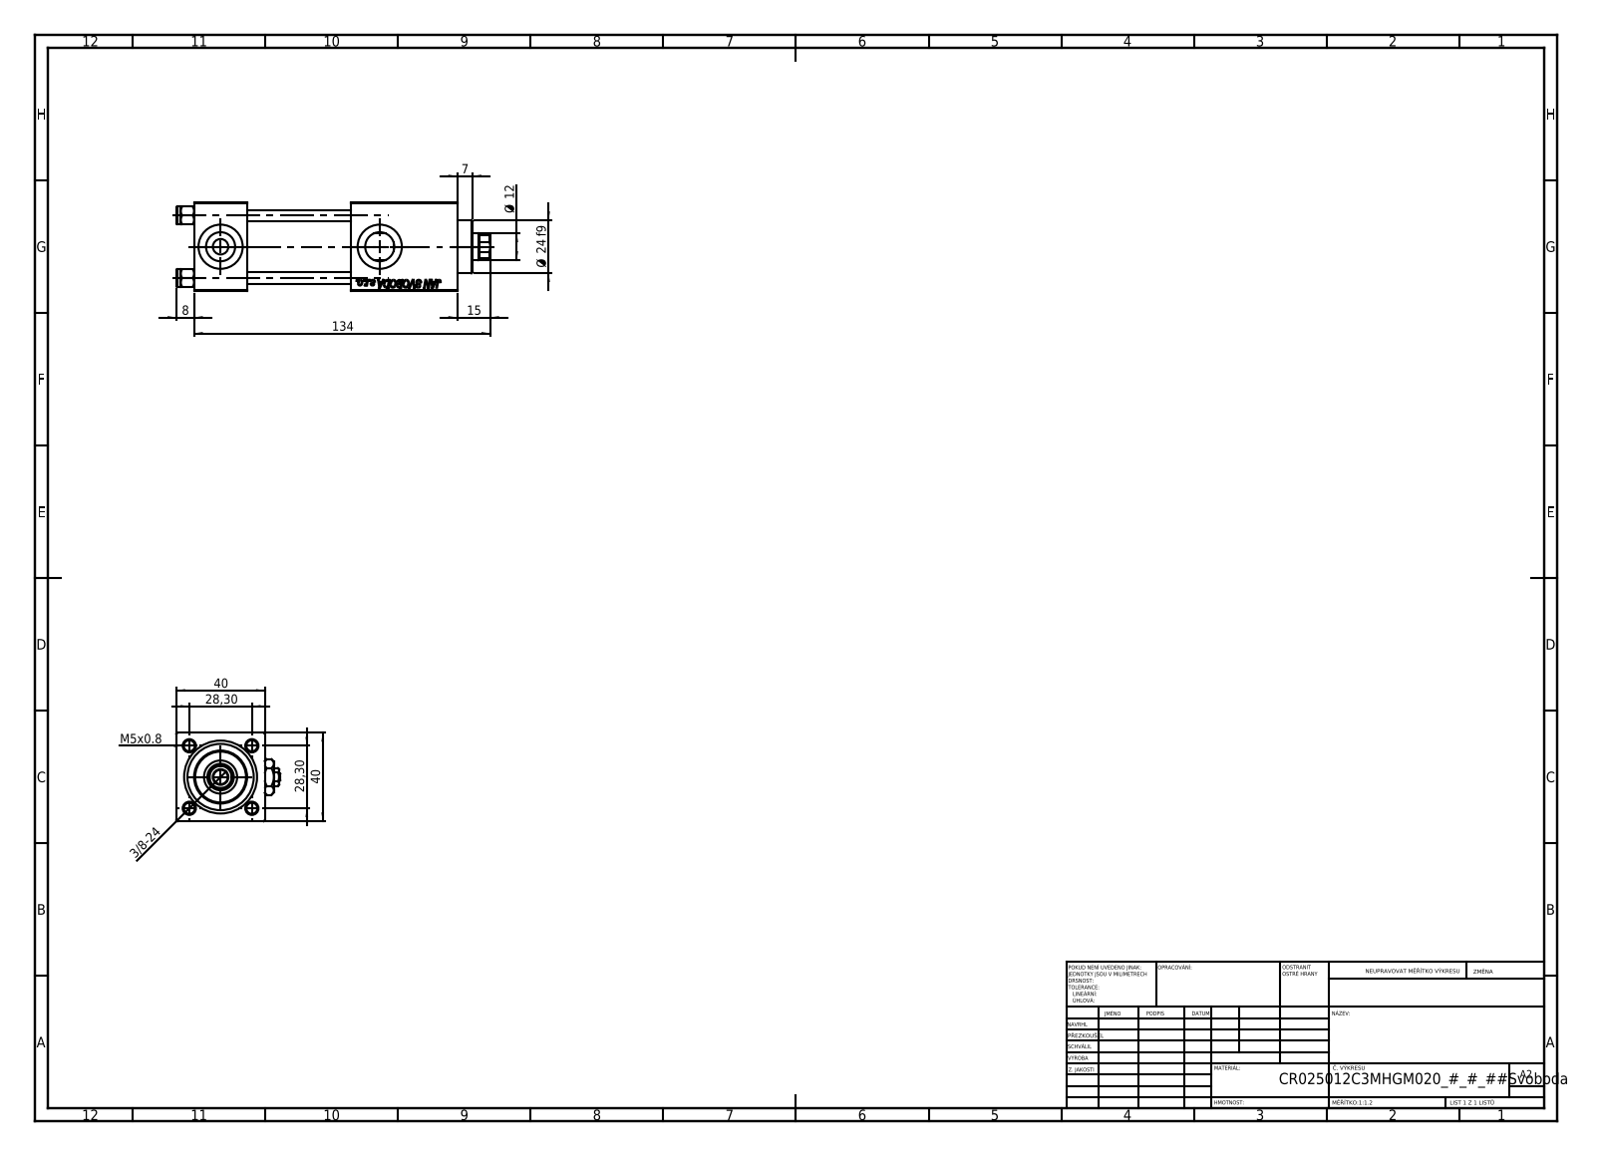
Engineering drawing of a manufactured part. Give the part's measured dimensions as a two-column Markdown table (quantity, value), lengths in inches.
| quantity | value |
| --- | --- |
| part name | V215CR_C_TYCINKA; V215_VC_A; V215CR_VCP_C; V215CR_C_Body (+2 more) |
| STEP written by | SolidWorks 2019 (CONFIG_CONTROL_DESIGN) |
| units | inches |
| bodies | 13 solids, 1248 faces (572 planar, 98 cylindrical, 578 other) |
| overall size | 5.591 × 1.85 × 1.575 |
| volume | 8.603 in³ |
| surface area | 87.12 in² |
| round holes (diameter × count) | 0.197 × 4, 0.787 × 3, 0.276 × 2, 0.518 × 2, 0.256 × 1, 0.472 × 1, 0.591 × 1, 0.984 × 1, 1.181 × 1 |
| round bosses / shafts (diameter × count) | 0.315 × 4, 1.22 × 1, 0.945 × 1 |
| partial cylindrical surfaces (radius × count) | 0.217 × 1 |
| main face-to-face distances | 1.575, 0.945, 1.567, 3.555, 2.61, 1.89, 1.85, 2.795, 0.76, 4.685 |
| hole center spacings | 0.788, 1.114, 1.576, 2.835 |
